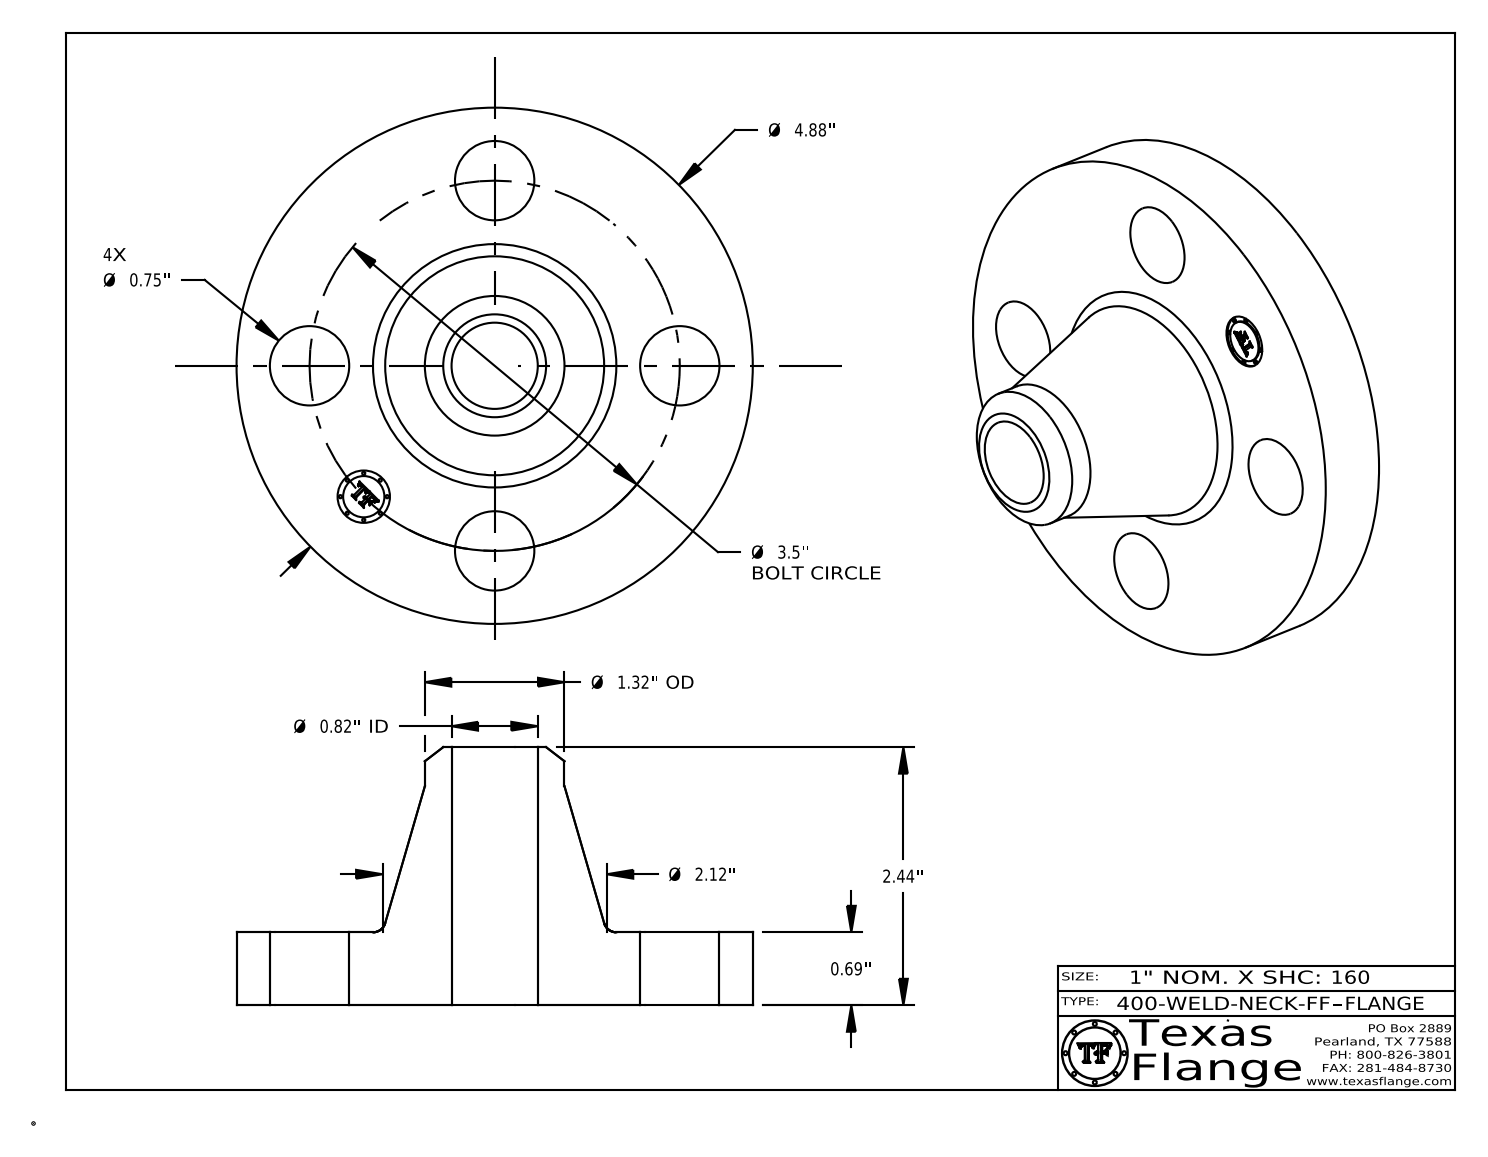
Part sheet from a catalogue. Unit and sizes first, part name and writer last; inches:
Units: inches
Overall size (bounding box): 4.88 × 4.88 × 2.44
Round holes (diameter × count): ⌀0.75 ×4, ⌀0.495 ×1, ⌀0.815 ×1
Round bosses / shafts (diameter × count): ⌀0.03 ×8, ⌀4.88 ×1, ⌀1.32 ×1, ⌀0.39 ×1
Main face-to-face distances: 0.69, 2.44, 1.75, 0.015, 0.675, 1.765, 0.148, 0.145, 0.027, 0.096
Hole centre spacings: 1.75, 2.475, 1.339, 3.233, 3.5
Volume: 14.15 in³ · Surface area: 62.83 in²
Bodies: 1 solid, 408 faces (368 planar, 34 cylindrical, 6 other)
Part name (STEP PRODUCT): 400-WELD-NECK-FF
STEP written by: CATIA V5 STEP AP214 (AUTOMOTIVE_DESIGN)
